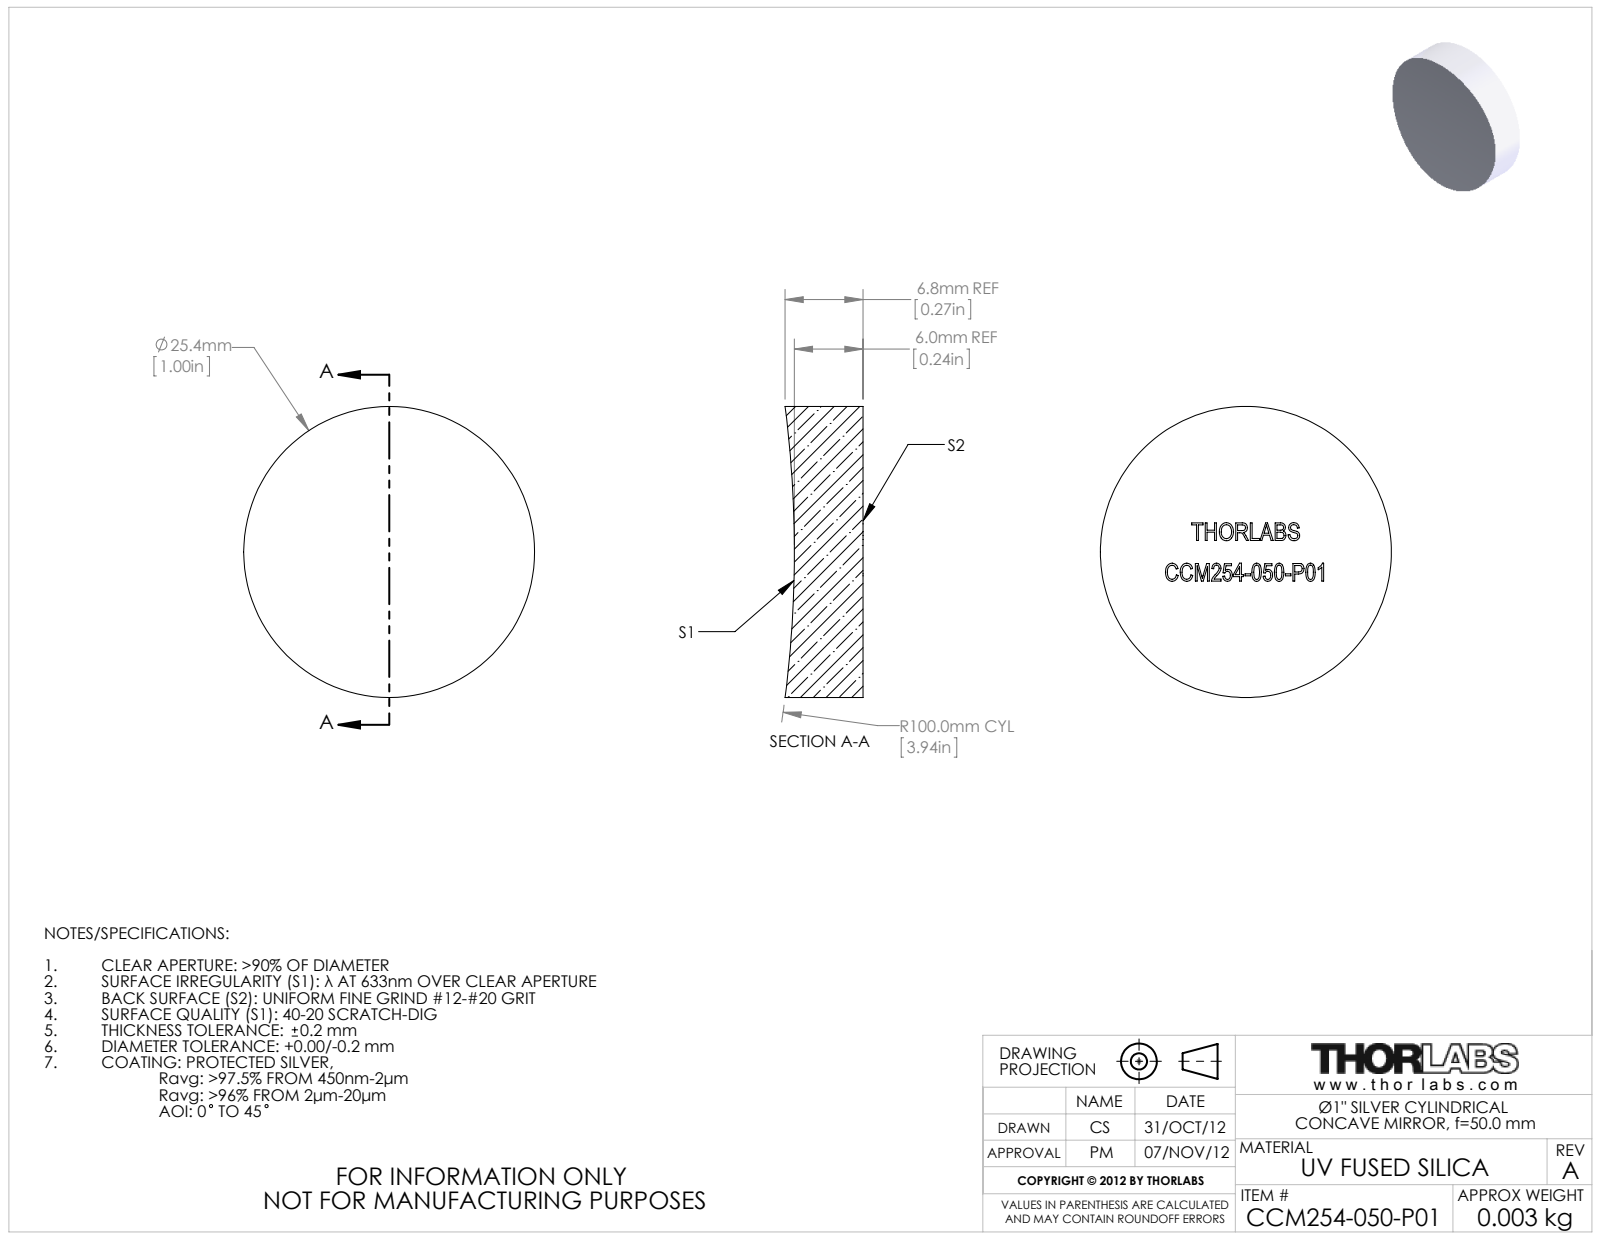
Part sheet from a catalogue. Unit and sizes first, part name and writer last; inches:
Units: inches
Overall size (bounding box): 1 × 1 × 0.268
Round bosses / shafts (diameter × count): ⌀1 ×1
Partial cylindrical surfaces — rounded edges, fillets, slot ends (radius × count): R3.937 ×1
Volume: 0.192 in³ · Surface area: 2.364 in²
Bodies: 1 solid, 37 faces (33 planar, 4 cylindrical, 0 other)
Part name (STEP PRODUCT): TTN005965-E0W
STEP written by: SolidWorks 2012 (CONFIG_CONTROL_DESIGN)
